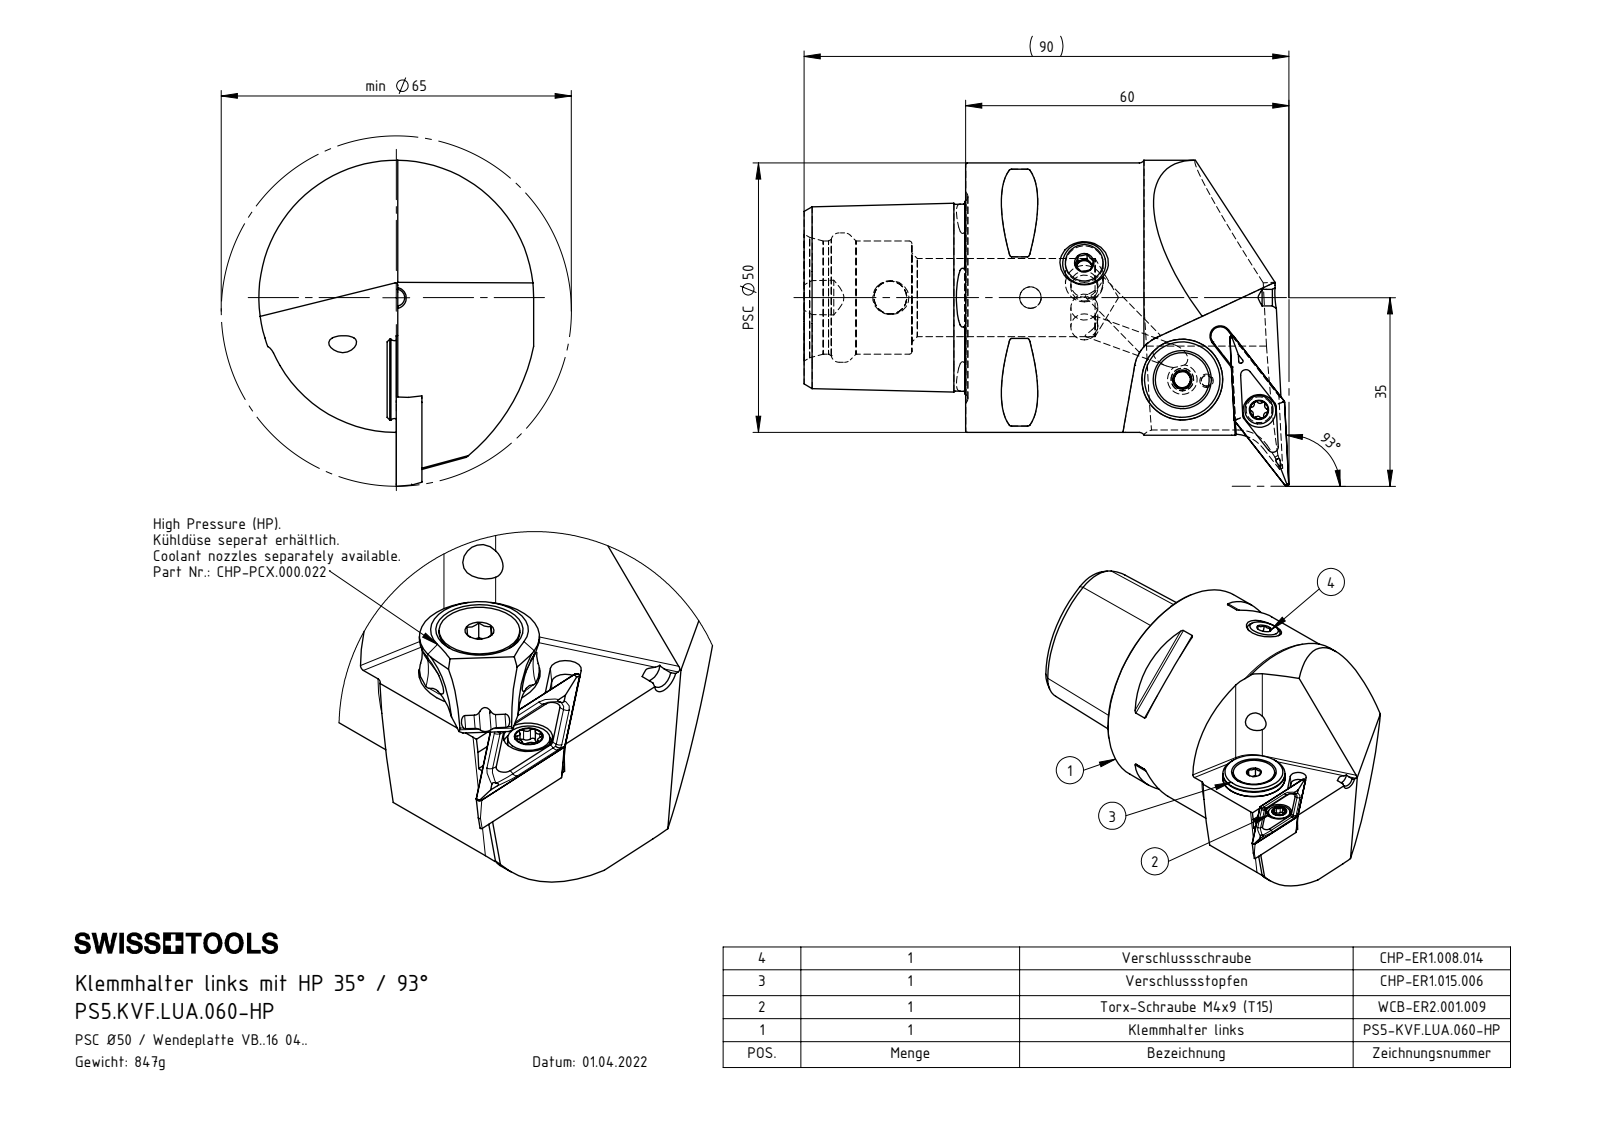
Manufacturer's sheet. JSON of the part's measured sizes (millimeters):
{"part_name": "ISO 8752 2x8; DIN 3771 - 13x1; CHP-ER1.008.014_A; DIN 7991 - M5x18 (+7 more)", "step_written_by": "SolidWorks 2017 (AUTOMOTIVE_DESIGN)", "units": "millimeters", "bodies": {"solids": 9, "faces": 486, "planar": 106, "cylindrical": 136, "other": 244}, "overall_size": [90, 60.5, 51], "volume_mm3": 107913, "surface_area_mm2": 23729, "round_holes": [[4.2, 2], [5, 2], [6.1, 2], [1.2, 1], [2, 1], [3, 1], [3.3, 1], [4, 1], [4.4, 1], [5.3, 1], [7, 1], [13, 1]], "round_bosses_or_shafts": [[50, 1], [14.85, 1], [13.4, 1], [10, 1], [8, 1], [5.5, 1], [5.25, 1], [5, 1]], "partial_cylinders_radius": [[0.5, 12], [1, 7], [0.34, 6], [0.59, 6], [6, 3], [0.15, 2], [1.1, 2], [1.2, 2]], "face_to_face_distances": [30, 4.46, 20.74, 25.2, 19.18, 20.7, 4.5, 44.4, 1.5, 3], "hole_center_spacings": [4.5, 11.13, 11.3, 15.31, 15.45, 26, 32.04, 36.15]}
